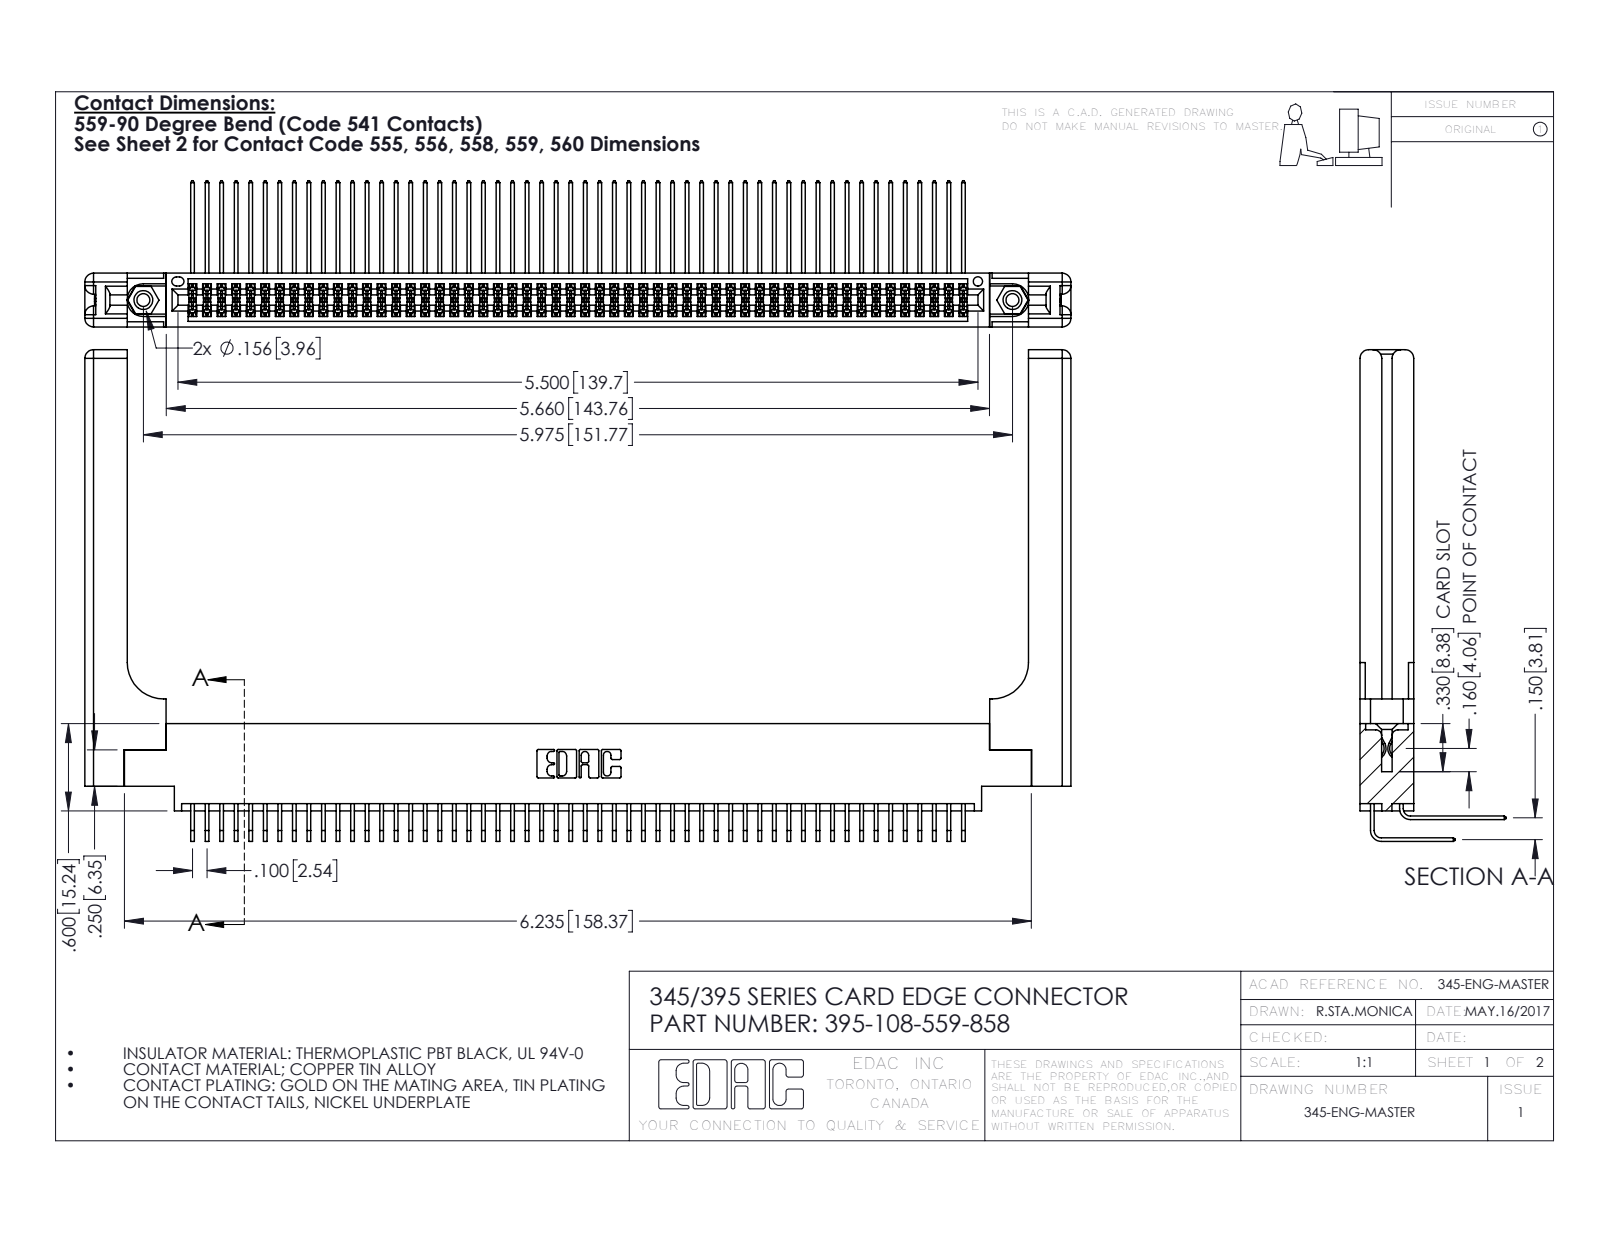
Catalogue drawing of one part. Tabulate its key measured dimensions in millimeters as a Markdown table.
| quantity | value |
| --- | --- |
| part name | 395-108-559-858; 345 Part_0.170 Offset - 0.156 Dia-TH; 345-220-058_345-220-058; 345-292-001_559 Tail - 2 (+2 more) |
| STEP written by | SolidWorks 2016 (CONFIG_CONTROL_DESIGN) |
| units | millimeters |
| bodies | 113 solids, 6002 faces (4012 planar, 1930 cylindrical, 60 other) |
| overall size | 172.2 × 85.8 × 25.5 |
| volume | 25 830 mm³ |
| surface area | 34 010 mm² |
| round holes (diameter × count) | 2.3 × 2, 3.2 × 2, 4 × 2, 1.6 × 1 |
| round bosses / shafts (diameter × count) | 3.9 × 2 |
| partial cylindrical surfaces (radius × count) | 0.2 × 162, 0.3 × 22, 1.5 × 16, 0.2 × 6, 0.8 × 6, 0.7 × 3, 0.4 × 2, 0.5 × 2 |
| main face-to-face distances | 1.8, 7.6, 9.4, 2.5, 6.9, 0.6, 5.1, 5.7, 4.4, 3.8 |
| hole center spacings | 6.9, 145.8, 151.8 |
